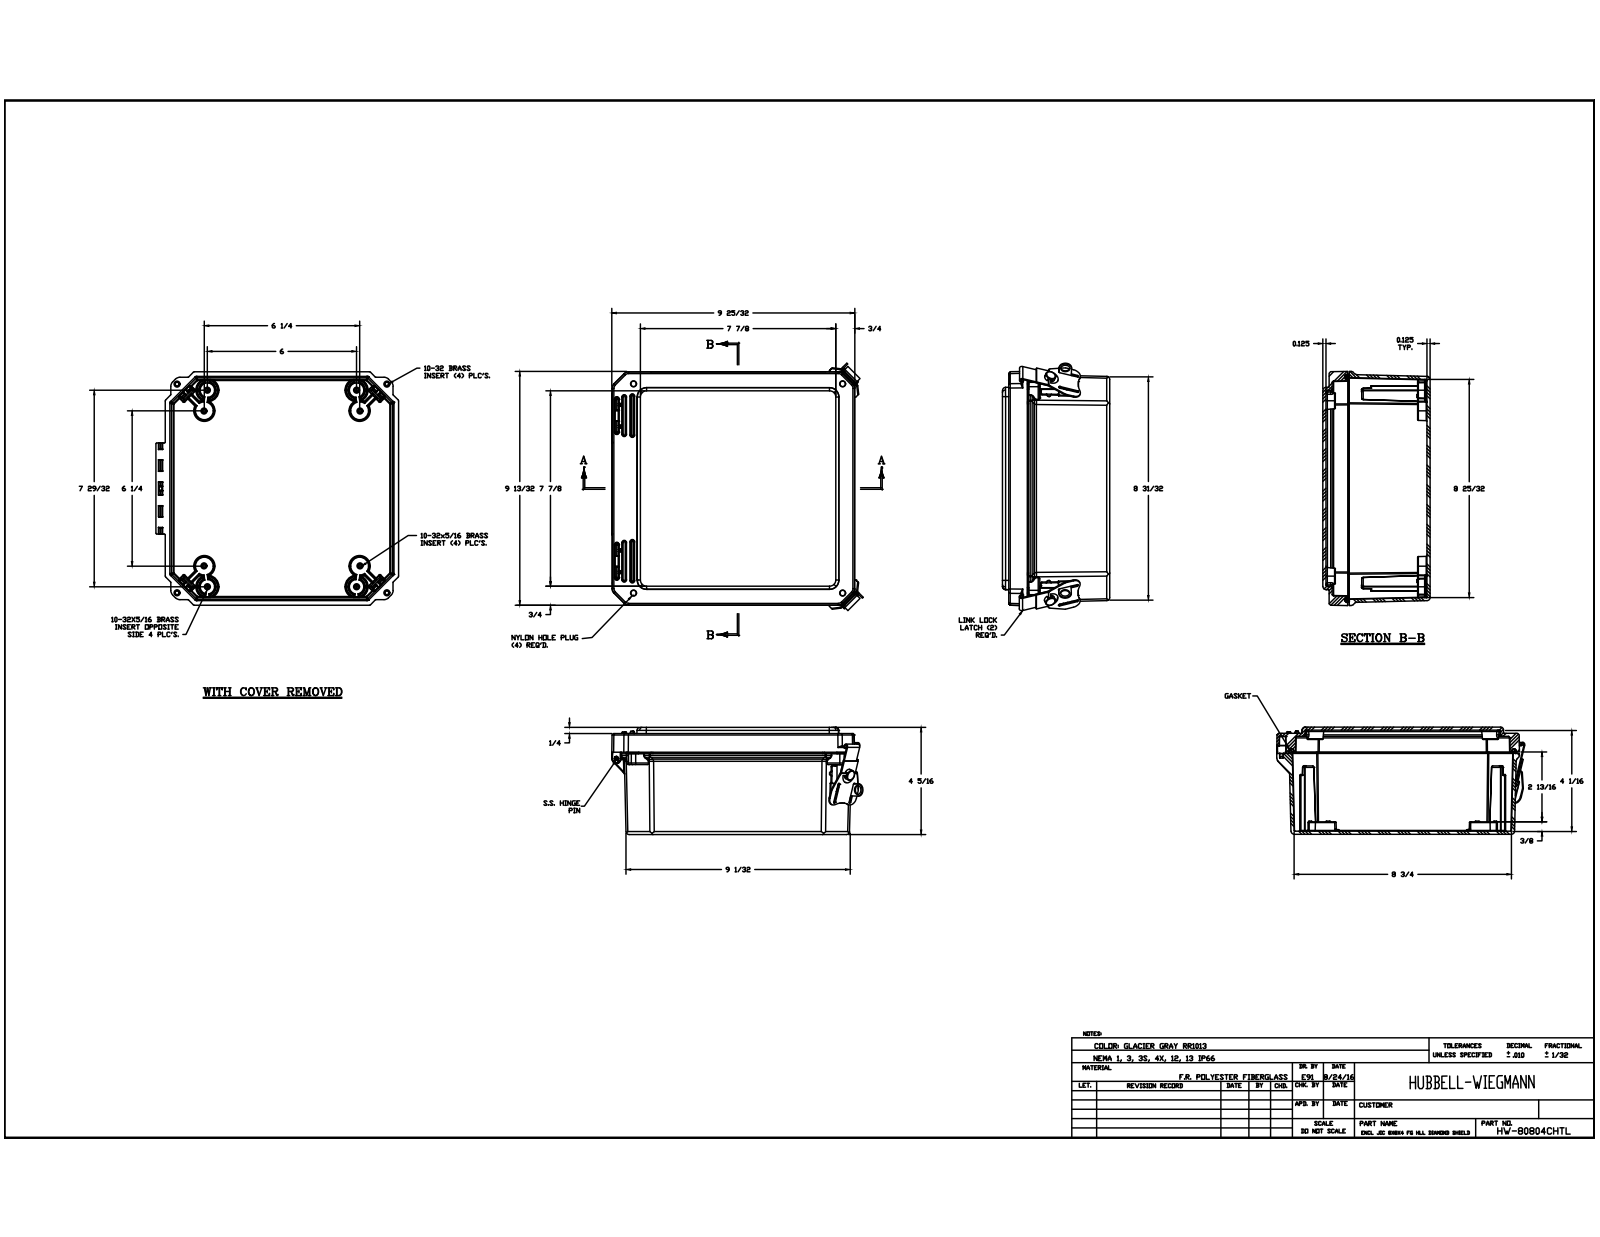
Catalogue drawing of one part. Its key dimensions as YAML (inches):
part_name: "HW-80804CHTL; DS080804BOX; BRASS INSERT-(; BRASS INSERT-(_1 (+7 more)"
step_written_by: "Autodesk Inventor 2017 (CONFIG_CONTROL_DESIGN)"
units: inches
bodies: {solids: 35, faces: 2202, planar: 751, cylindrical: 855, other: 596}
overall_size: [10.262, 10.201, 4.31]
volume: 52.43
surface_area: 742.4
round_holes:
  - {diameter: 0.156, count: 16}
  - {diameter: 0.152, count: 8}
  - {diameter: 0.098, count: 4}
  - {diameter: 0.15, count: 4}
  - {diameter: 0.252, count: 4}
  - {diameter: 0.253, count: 4}
  - {diameter: 0.05, count: 2}
  - {diameter: 0.12, count: 2}
  - {diameter: 0.219, count: 2}
  - {diameter: 0.227, count: 2}
  - {diameter: 0.313, count: 2}
  - {diameter: 0.363, count: 2}
round_bosses_or_shafts:
  - {diameter: 0.246, count: 16}
  - {diameter: 0.87, count: 4}
  - {diameter: 0.209, count: 4}
  - {diameter: 0.2, count: 4}
  - {diameter: 0.05, count: 4}
  - {diameter: 0.135, count: 3}
  - {diameter: 0.6, count: 2}
  - {diameter: 0.435, count: 2}
partial_cylinders:
  - {radius: 0.01, count: 129}
  - {radius: 0.005, count: 80}
  - {radius: 0.02, count: 65}
  - {radius: 0.03, count: 42}
  - {radius: 0.125, count: 34}
  - {radius: 0.039, count: 28}
  - {radius: 0.063, count: 28}
  - {radius: 0.03, count: 24}
face_to_face_distances: [0.125, 4.185, 4.31, 4.061, 0.124, 0.25, 3.935, 0.125, 0.375, 4.06]
hole_center_spacings: [6.663, 6.25, 6.25, 9.406, 7.399, 0.837, 7.08, 7.411]
